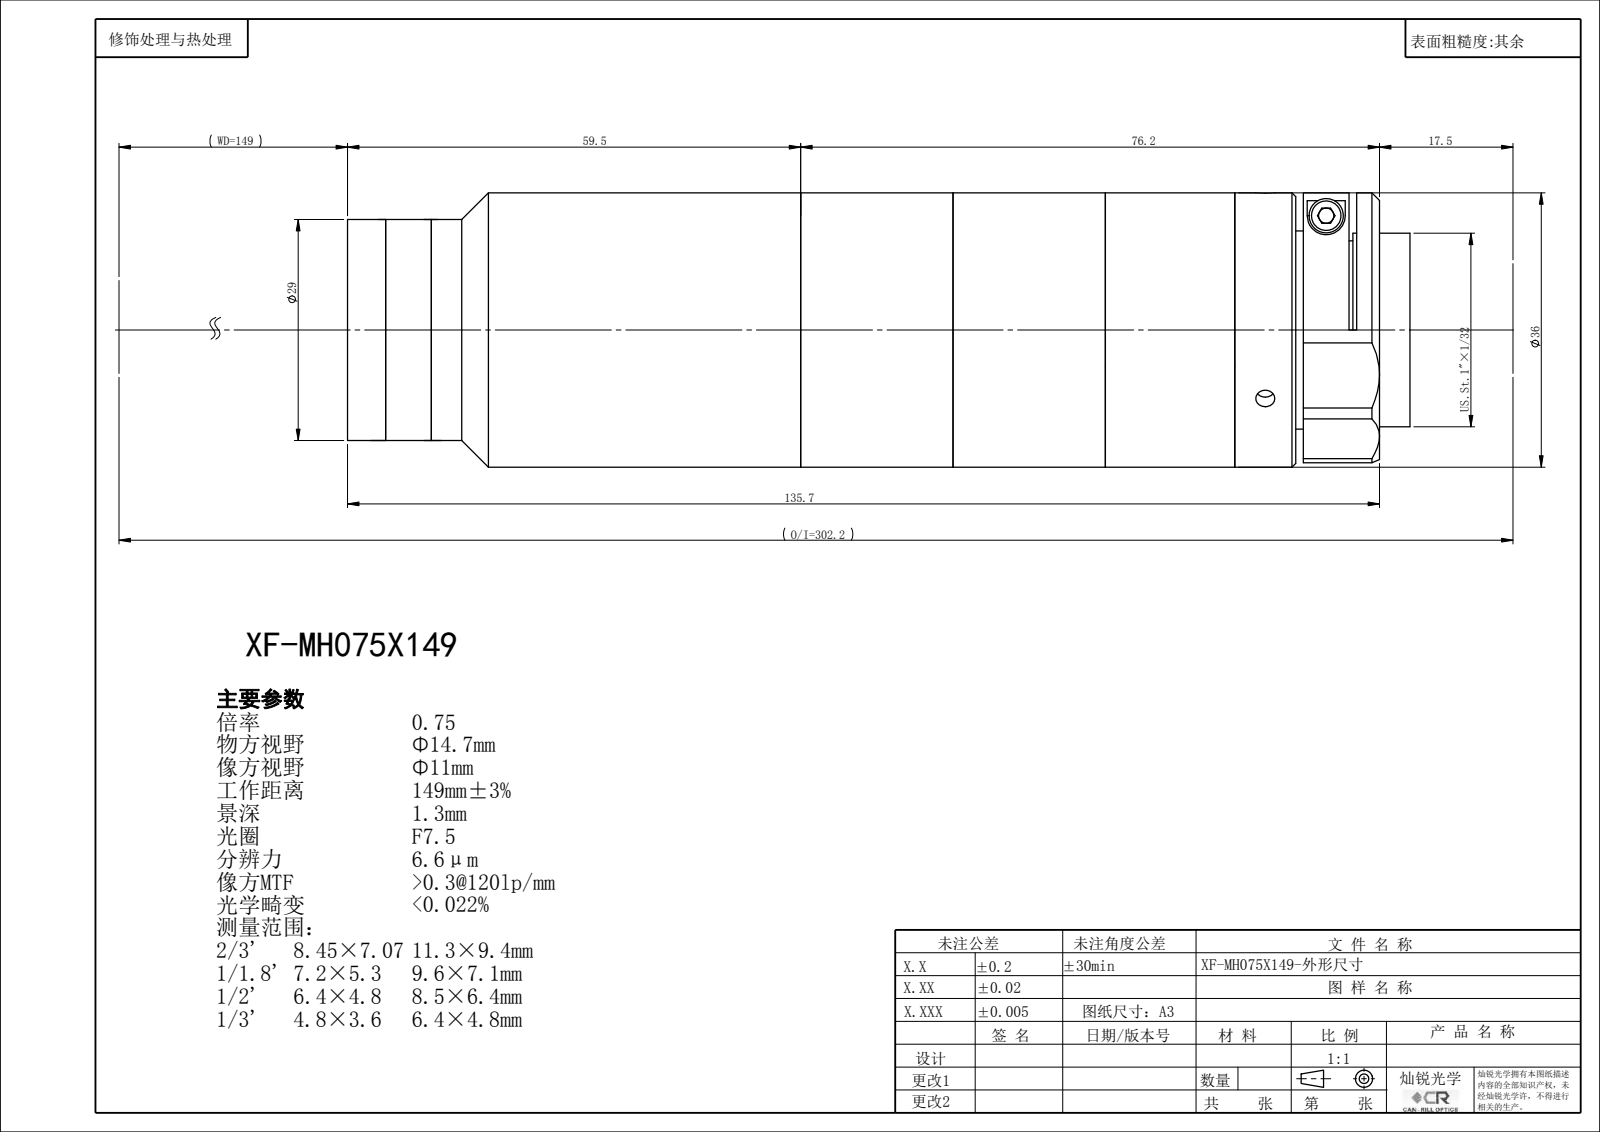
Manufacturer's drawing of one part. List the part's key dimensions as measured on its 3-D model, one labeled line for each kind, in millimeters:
Part name (STEP PRODUCT): XF-MH075X149
STEP written by: SolidWorks 2022 (CONFIG_CONTROL_DESIGN)
Units: millimetres
Bodies: 0 solids, 126 faces (60 planar, 44 cylindrical, 22 other)
Overall size (bounding box): 139.66 × 36 × 36
Round holes (diameter × count): ⌀2.5 ×3, ⌀18 ×1, ⌀22.4 ×1, ⌀24 ×1, ⌀24.9 ×1, ⌀26.4 ×1
Round bosses / shafts (diameter × count): ⌀36 ×1, ⌀34 ×1, ⌀29 ×1, ⌀25.4 ×1
Main face-to-face distances: 19.16, 1.5, 17.66, 17, 34.66, 36.16, 40, 57, 74.66, 76.16
